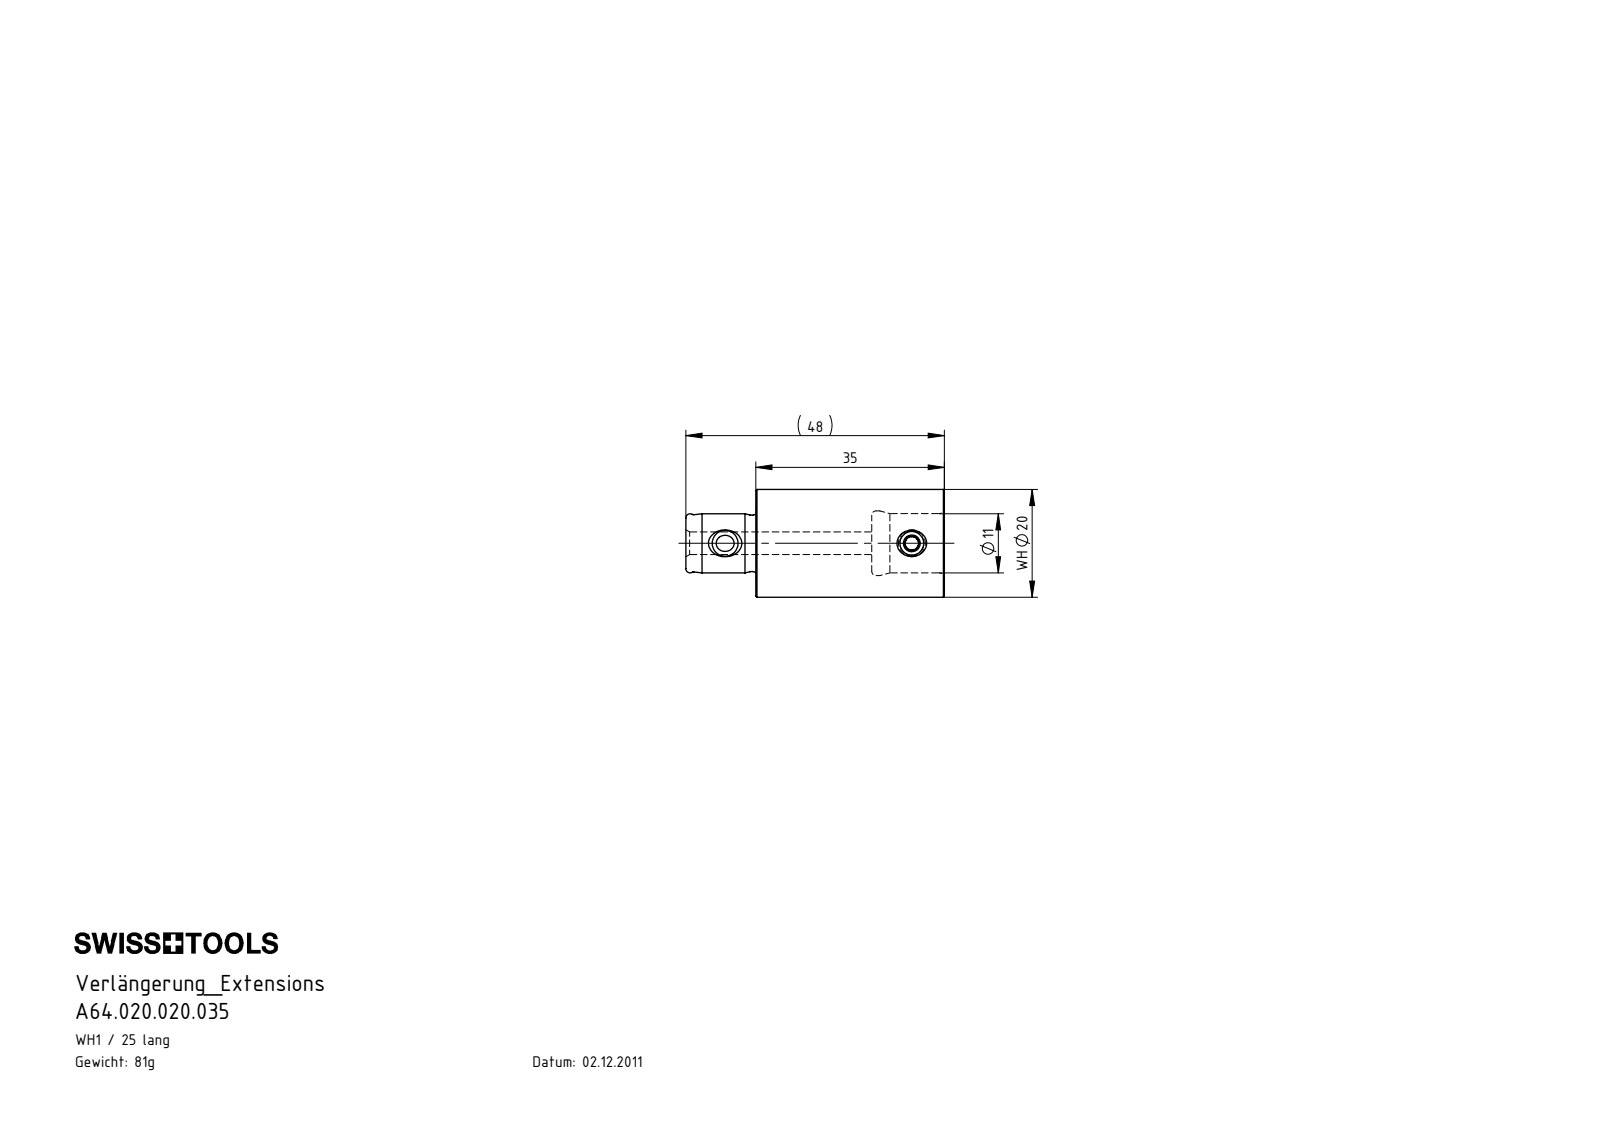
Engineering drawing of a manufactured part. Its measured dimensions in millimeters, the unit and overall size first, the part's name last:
Units: millimetres
Overall size (bounding box): 48 × 20 × 20
Round holes (diameter × count): ⌀4.2 ×1, ⌀4.5 ×1, ⌀11 ×1, ⌀12 ×1
Round bosses / shafts (diameter × count): ⌀20 ×1, ⌀10.5 ×1, ⌀5 ×1
Main face-to-face distances: 35, 21.5, 13.5, 13, 34.5, 48, 2.5, 7.5, 5
Volume: 10 379 mm³ · Surface area: 4 333 mm²
Bodies: 2 solids, 71 faces (13 planar, 16 cylindrical, 42 other)
Part name (STEP PRODUCT): WH1-WH1.001.035_A; WH1-ER1.001.008; WH1-WH1.001.035
STEP written by: SolidWorks 2015 (AUTOMOTIVE_DESIGN)
